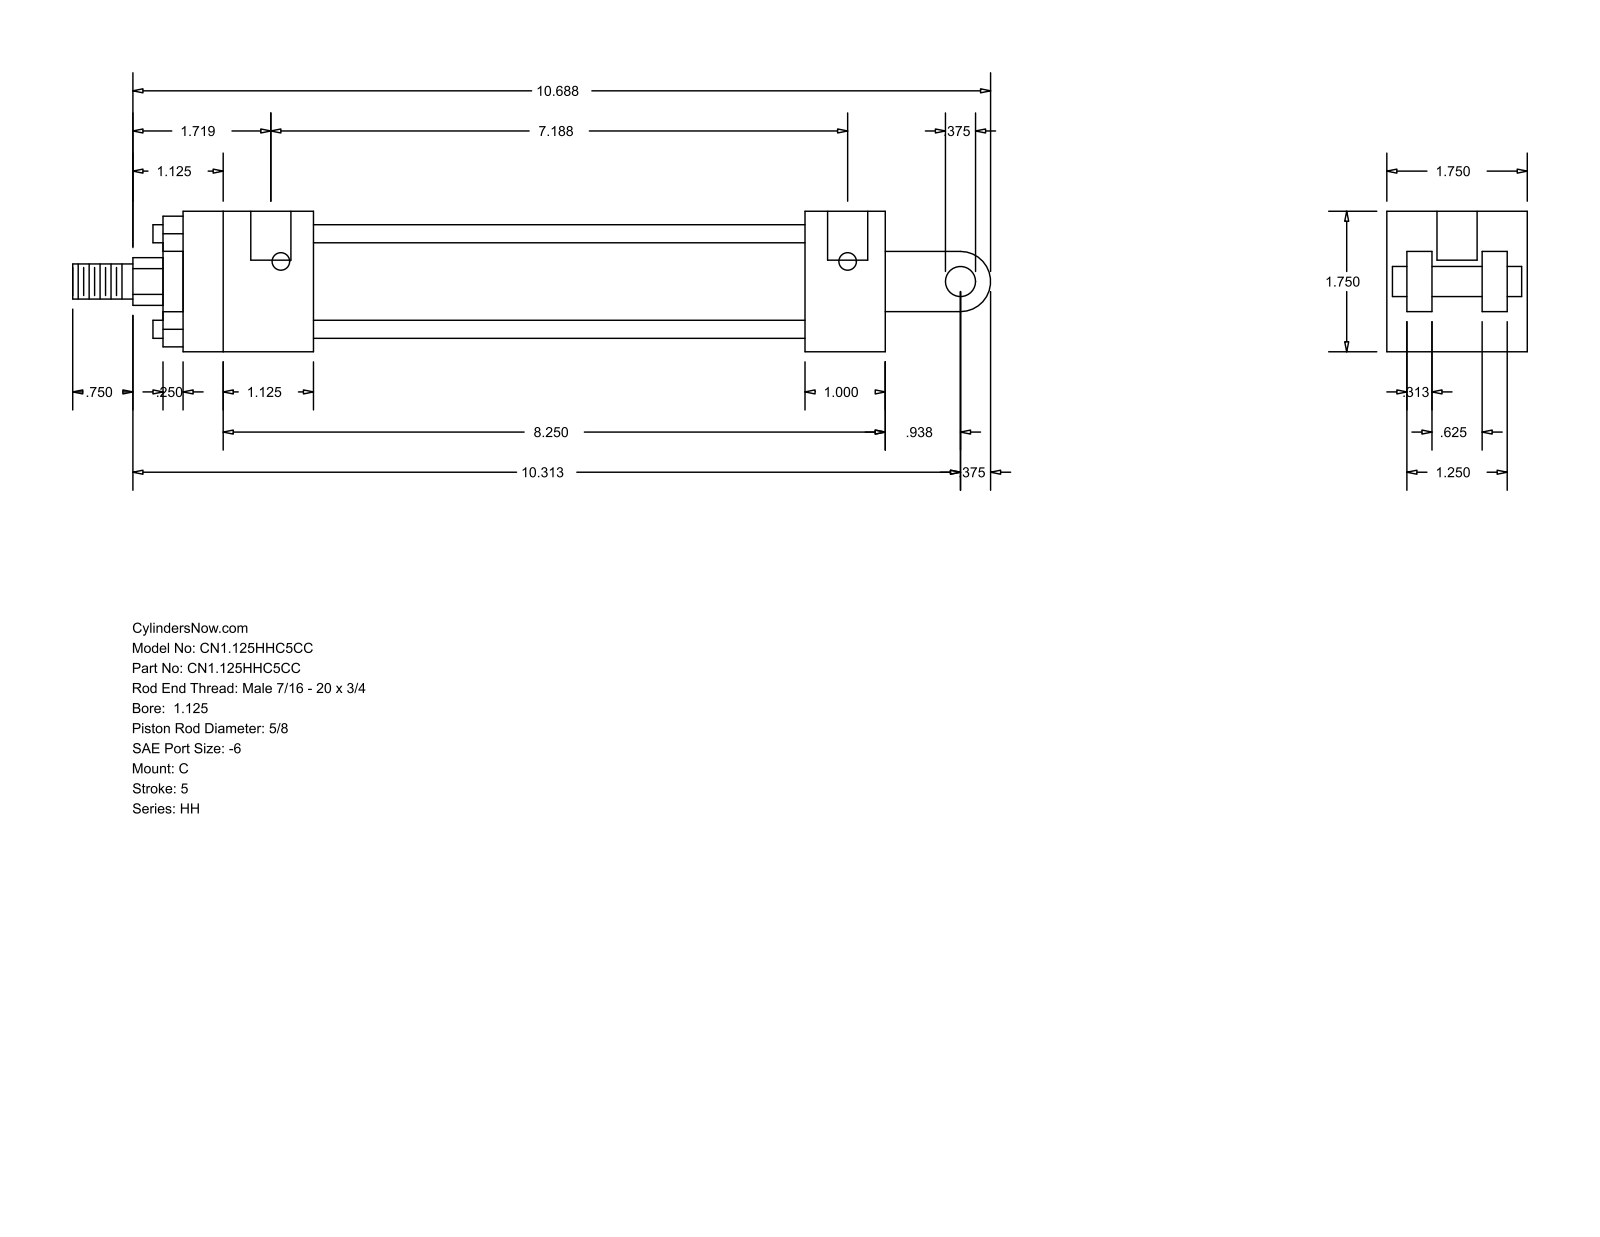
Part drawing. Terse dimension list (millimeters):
name: HH_C__0112_0.625
written by: GSSL Pune (CONFIG_CONTROL_DESIGN)
unit: mm
bodies: 0 solids, 99 faces (70 planar, 29 cylindrical, 0 other)
size: 290.51 × 44.45 × 44.45
holes: 4× ⌀5.56, 2× ⌀12.7
bosses: 4× ⌀5.71, 1× ⌀34.92, 1× ⌀28.57, 1× ⌀15.88, 1× ⌀11.11, 1× ⌀9.53
rounds: 1× R7.54, 1× R9.53
face distances: 44.46, 6.35, 31.76, 14.29, 25.4, 30.17, 38.11, 7.94, 23.82, 12.7
hole spacings: 179.39, 3.17, 182.56
